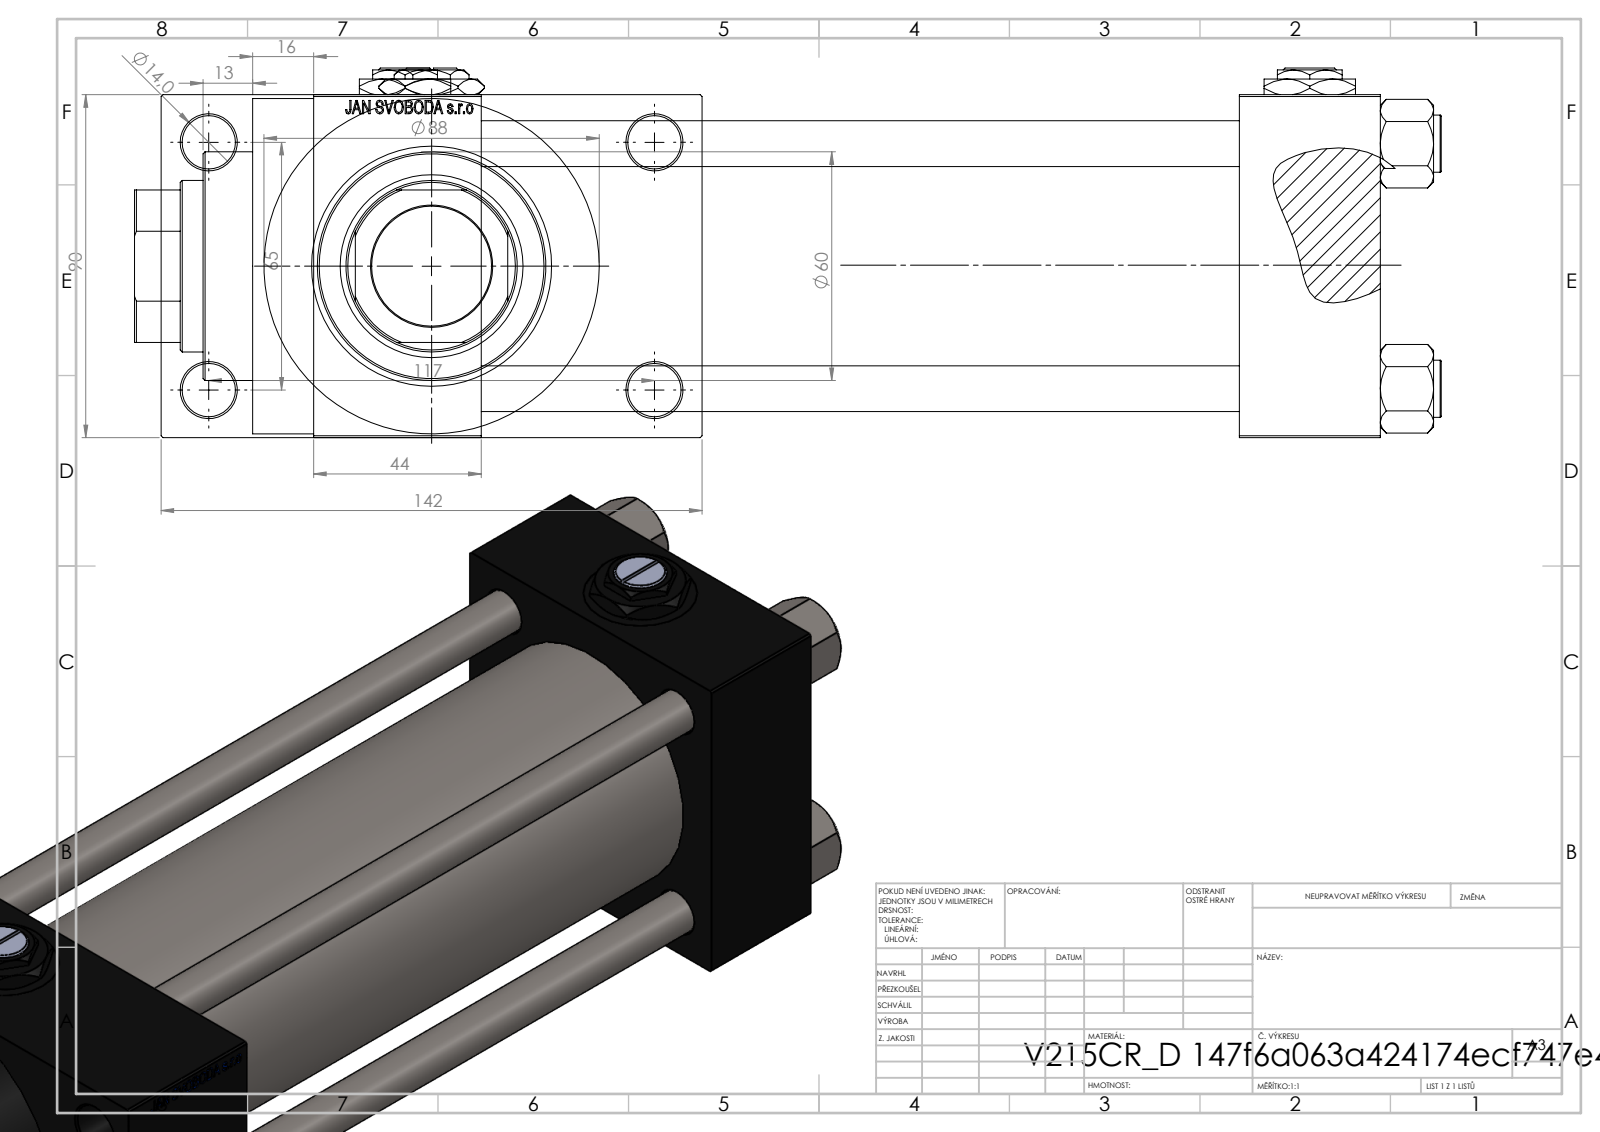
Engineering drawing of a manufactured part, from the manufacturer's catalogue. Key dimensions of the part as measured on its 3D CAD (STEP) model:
Part name (STEP PRODUCT): V215_VC_A; NUT_M5_D; V215CR_D_TYCINKA; Zatka_pro_OIL_PORT (+2 more)
STEP written by: SolidWorks 2019 (CONFIG_CONTROL_DESIGN)
Units: millimetres
Bodies: 13 solids, 1203 faces (544 planar, 97 cylindrical, 562 other)
Overall size (bounding box): 343 × 142 × 97
Volume: 1 527 000 mm³ · Surface area: 315 972 mm²
Round holes (diameter × count): ⌀12 ×4, ⌀14 ×4, ⌀20.96 ×4, ⌀30 ×4, ⌀7 ×3, ⌀31.5 ×1, ⌀45 ×1, ⌀48 ×1, ⌀50 ×1, ⌀60 ×1, ⌀63 ×1
Round bosses / shafts (diameter × count): ⌀15 ×4, ⌀88 ×1, ⌀69 ×1
Partial cylindrical surfaces — rounded edges, fillets, slot ends (radius × count): R22 ×1
Main face-to-face distances: 90, 199, 37, 236, 26, 44, 280, 243, 116, 60
Hole centre spacings: 26.35, 45.47, 64.3, 66.92, 69.81, 90.65, 111.34, 65
